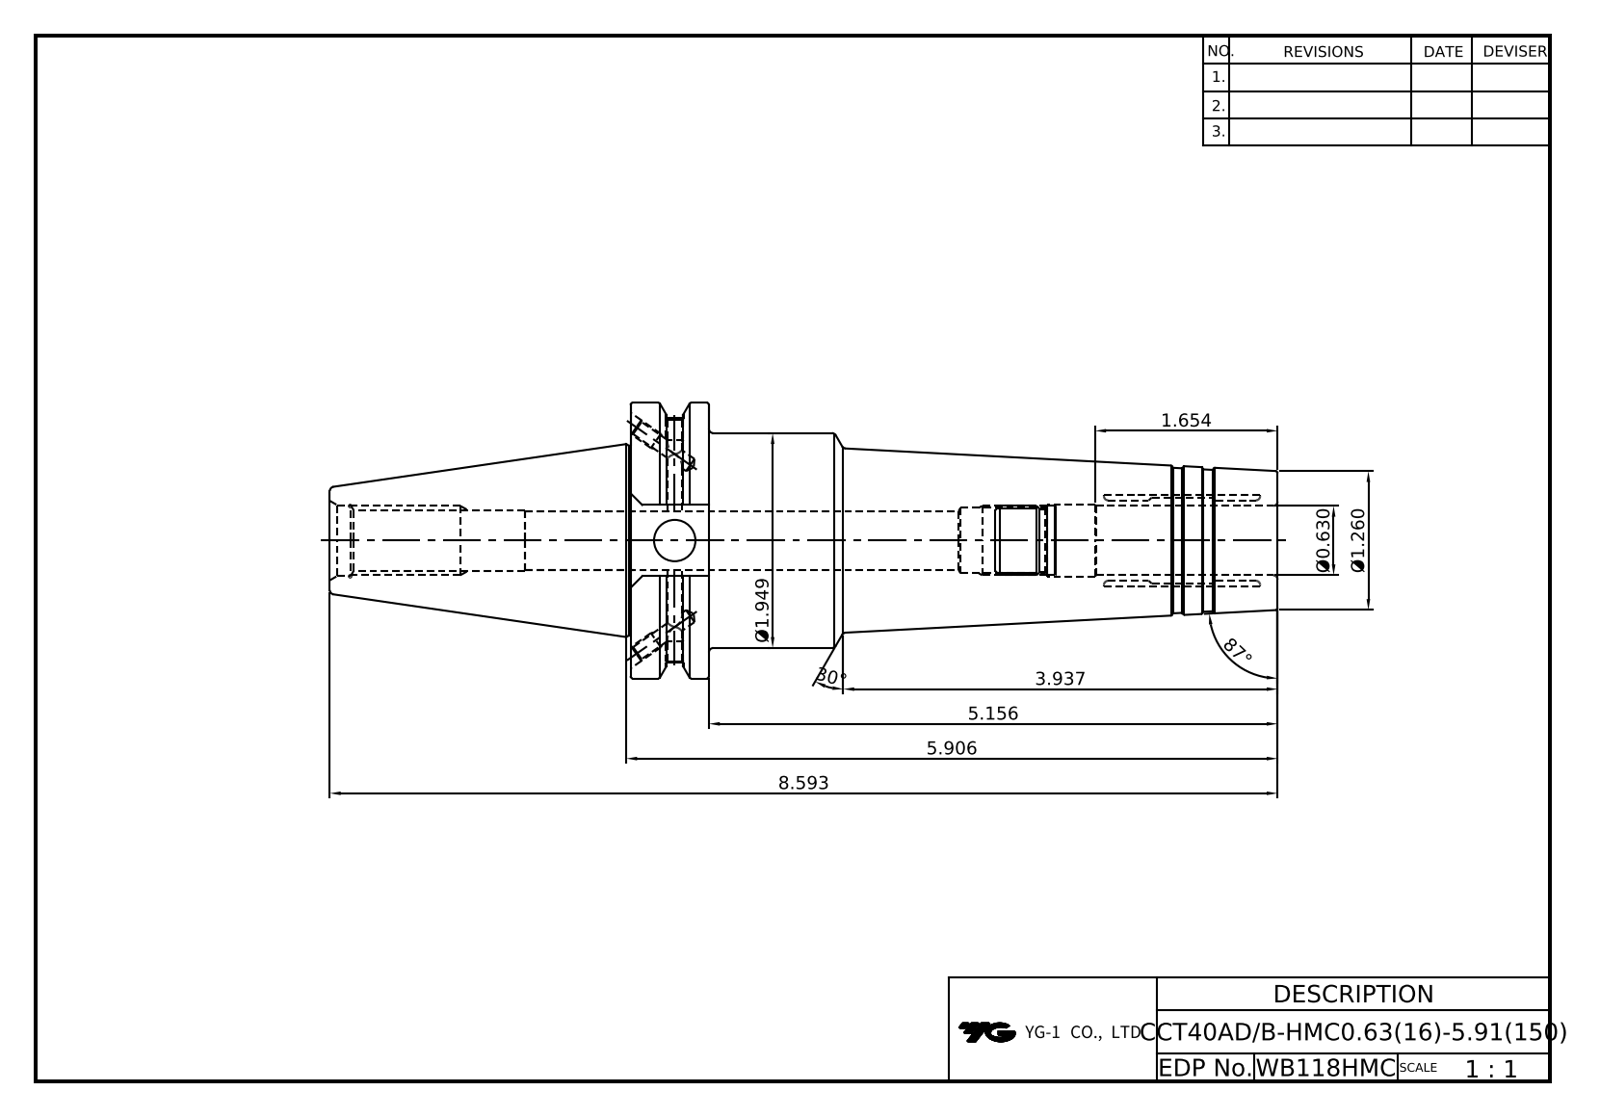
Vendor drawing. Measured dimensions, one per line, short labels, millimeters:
name: LO-CCT40ADB-HMC16-150
written by: Autodesk Inventor 2022 (AUTOMOTIVE_DESIGN)
unit: mm
bodies: 1 solid, 106 faces (35 planar, 30 cylindrical, 41 other)
size: 218.25 × 63.5 × 61.09
volume: 251 453 mm³; area: 42 437 mm²
holes: 4× ⌀3.24, 2× ⌀4, 2× ⌀4.2, 1× ⌀9.53, 1× ⌀10.92, 1× ⌀13, 1× ⌀13.39, 1× ⌀16, 1× ⌀16.3, 1× ⌀16.6
bosses: 1× ⌀63.5, 1× ⌀49.5, 1× ⌀43.8
rounds: 1× R8.19, 1× R28.15
face distances: 18.05, 149, 130.95, 47.6, 16.38, 69.25, 87.3, 218.25, 167.25, 98
